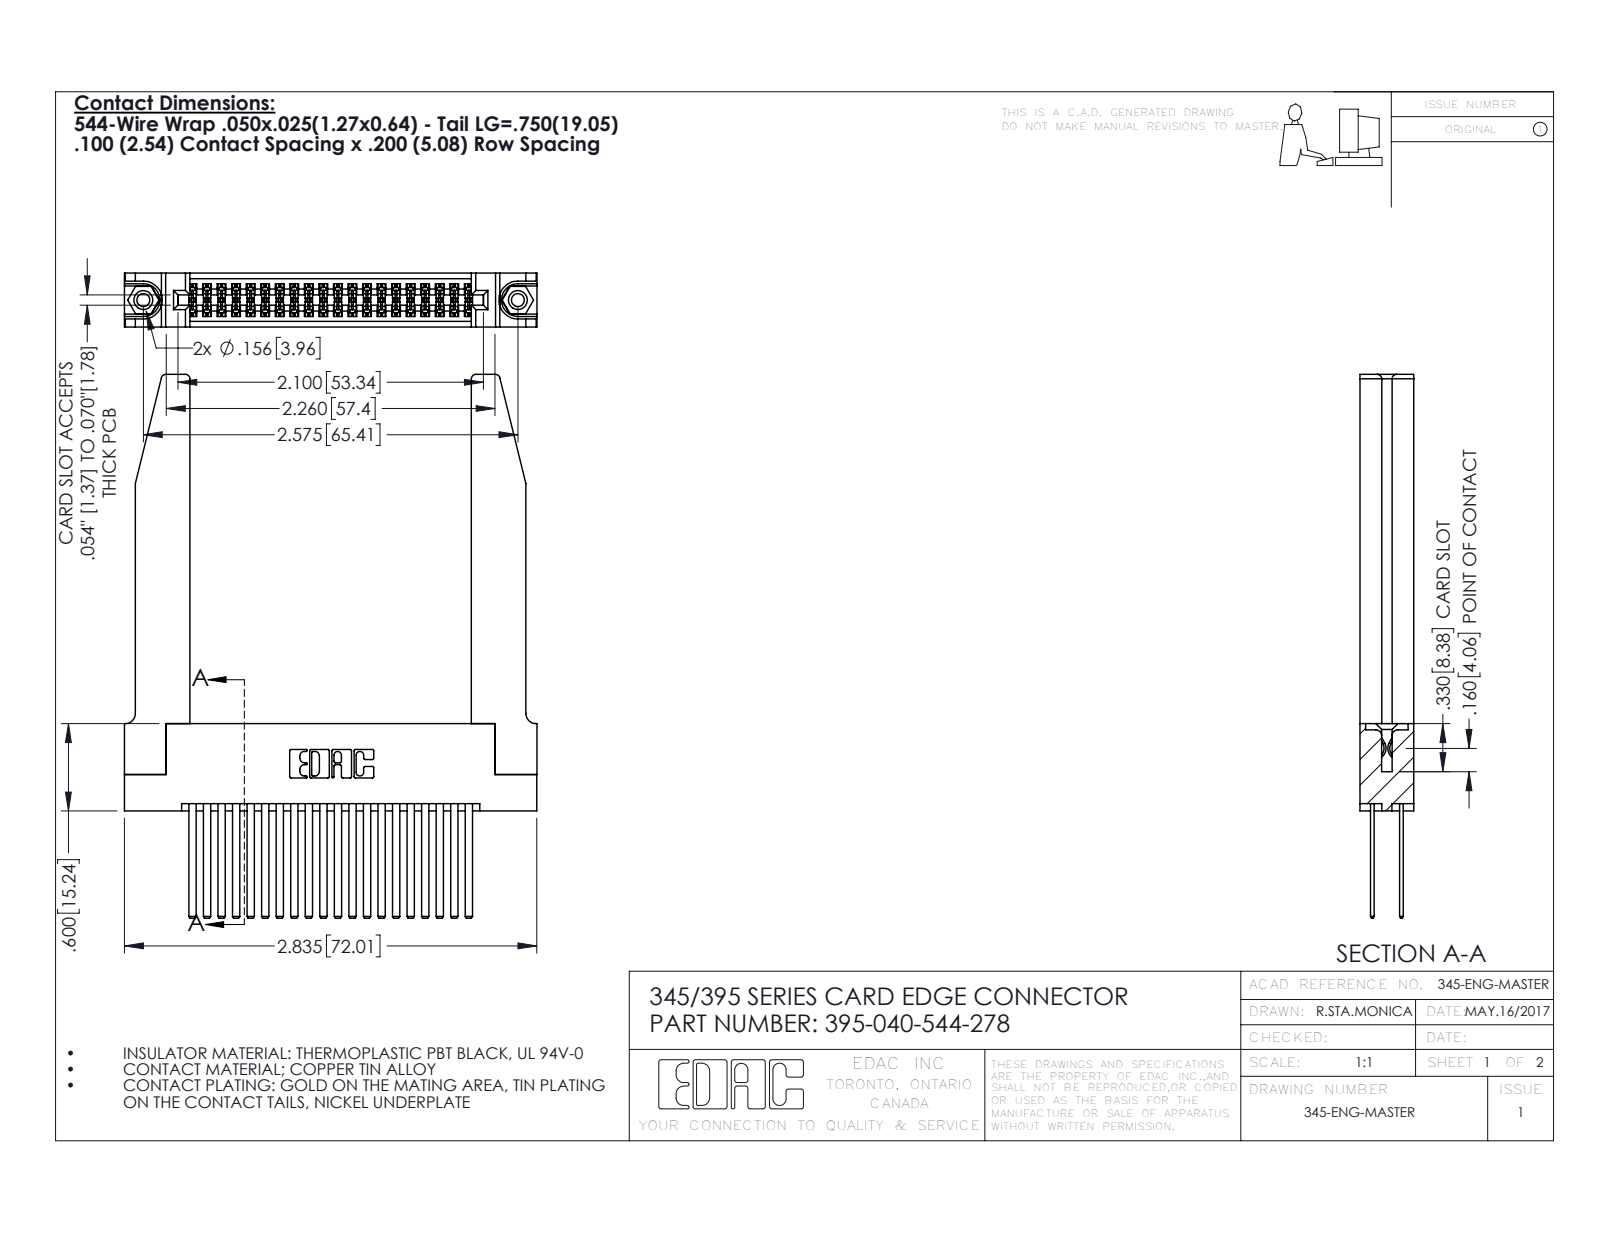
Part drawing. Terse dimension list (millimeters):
name: 345 Part_Flush Mounting Lugs - 0.156 Dia-TH; 345-292-001_345-293-144; 345-250-001_345-250-001-102; 395-040-544-278 (+1 more)
written by: SolidWorks 2016 (CONFIG_CONTROL_DESIGN)
unit: mm
bodies: 45 solids, 2120 faces (1382 planar, 686 cylindrical, 52 other)
size: 94.9 × 72 × 9.4
volume: 15 100 mm³; area: 18 930 mm²
holes: 2× ⌀2.3, 2× ⌀3.2, 2× ⌀4, 1× ⌀1.6
bosses: 2× ⌀3.9
rounds: 60× R0.2, 22× R0.3, 8× R0.8, 6× R0.2, 6× R0.8, 3× R0.7, 2× R0.4, 2× R0.5
face distances: 1.8, 7.6, 9.4, 5.1, 2.5, 6.9, 0.6, 5.7, 4.4, 3.8
hole spacings: 6.9, 59.5, 65.4
